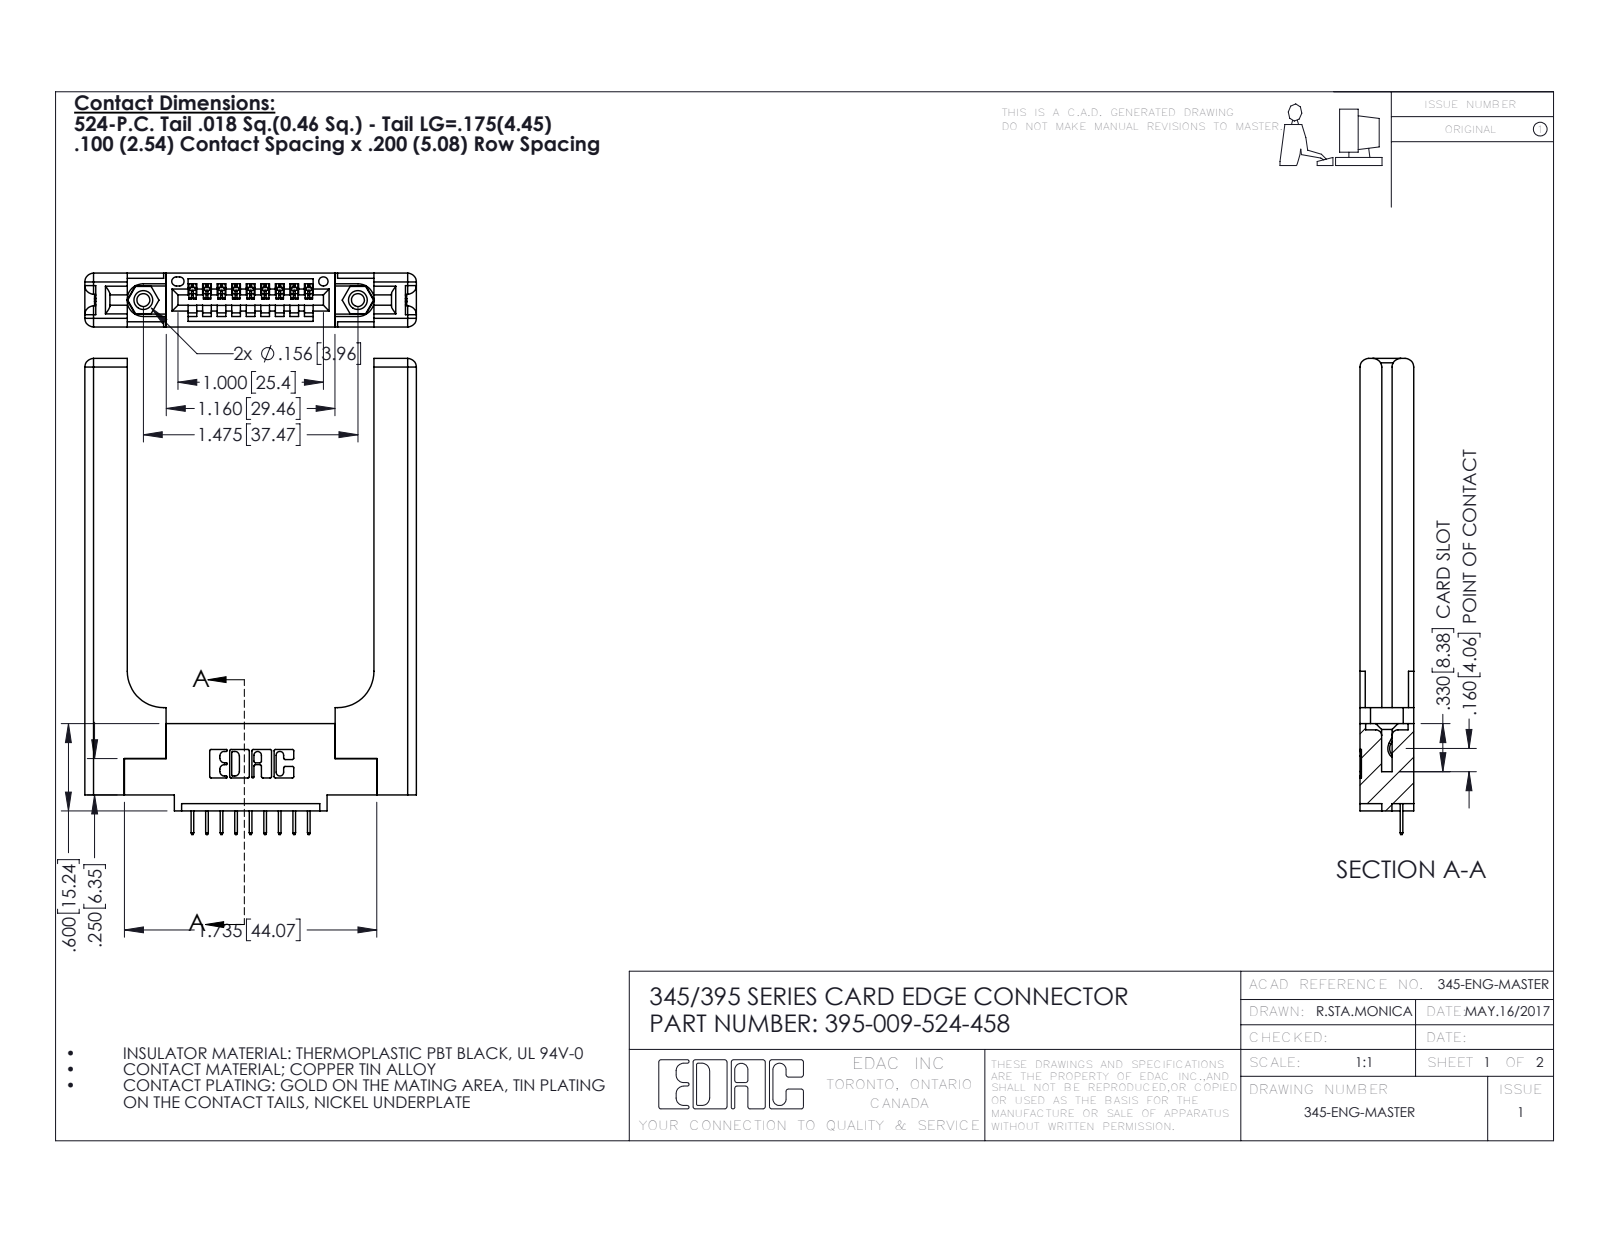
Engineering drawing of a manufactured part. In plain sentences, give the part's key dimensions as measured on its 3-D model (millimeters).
The part is named "345-220-058_345-220-058; 345-250-001_345-250-001-102; 395-009-524-458; 345-292-001_345-293-124 (+1 more)". Its 3-D file was written by "SolidWorks 2016 (CONFIG_CONTROL_DESIGN)". It is 14 solids with 944 faces: 646 planar, 238 cylindrical and 60 other. Overall it measures 83.1 by 57.9 by 9.4 millimeters. Its volume is 13 600 cubic millimeters and its surface area 11 630 square millimeters. Round holes: 2 of diameter 2.3, 2 of diameter 3.2, 2 of diameter 4, 1 of diameter 1.6. Round bosses or shafts: 2 of diameter 3.9. Partial cylindrical surfaces (rounded edges, fillets, slot ends): 22 of radius 0.3, 18 of radius 0.2, 16 of radius 1.5, 6 of radius 0.2, 6 of radius 0.8, 3 of radius 0.7, 2 of radius 0.8, 2 of radius 0.8. The main face-to-face distances are 9.4, 3.8, 5.6, 1.8, 3.8, 2, 7.6, 43.1, 1.8, 7.4. The hole center spacings are 6.9, 31.6, 37.5.
